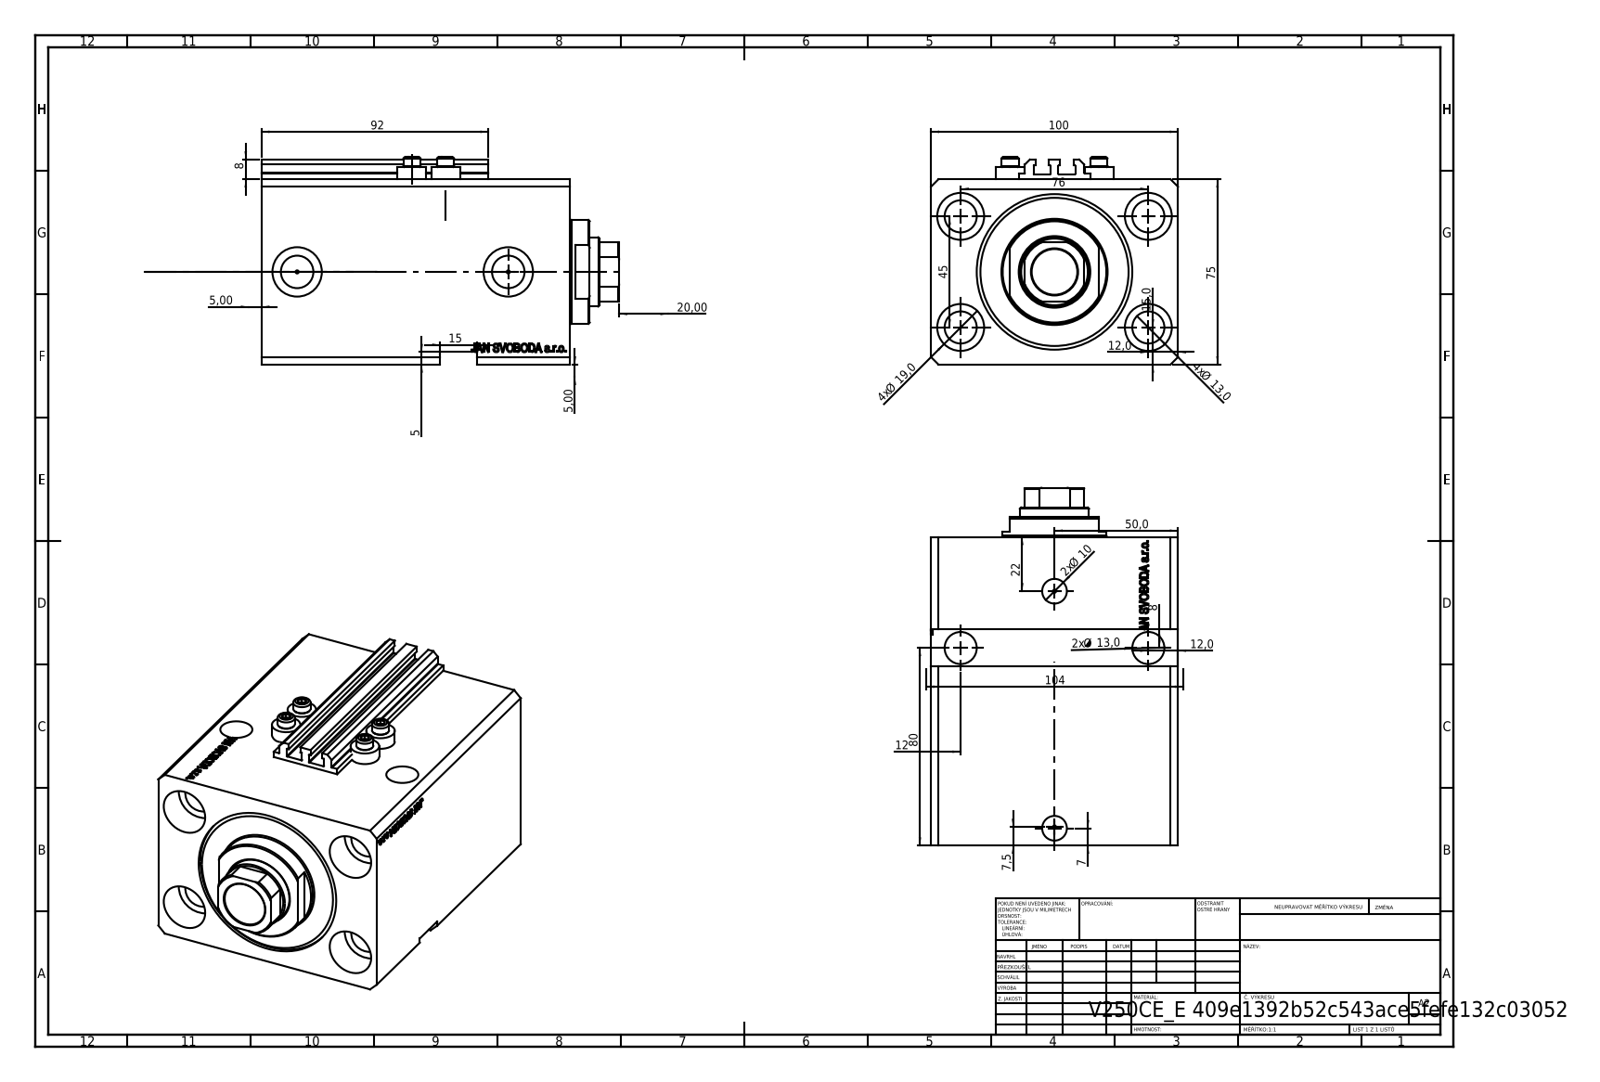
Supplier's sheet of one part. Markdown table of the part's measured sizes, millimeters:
| quantity | value |
| --- | --- |
| part name | V250CE_C_VCP; V250CE_E_Body; ALLEN BOLT V250CE; V250CE_VC_E |
| STEP written by | SolidWorks 2019 (CONFIG_CONTROL_DESIGN) |
| units | millimeters |
| bodies | 8 solids, 1088 faces (535 planar, 126 cylindrical, 427 other) |
| overall size | 144.9 × 100 × 84 |
| volume | 782 818 mm³ |
| surface area | 149 099 mm² |
| round holes (diameter × count) | 13 × 6, 1.25 × 4, 4 × 4, 19 × 4, 10 × 2, 13.16 × 2, 20 × 2, 18.5 × 1, 28 × 1, 50 × 1, 63 × 1 |
| round bosses / shafts (diameter × count) | 11.6 × 4, 7 × 4, 42 × 1 |
| partial cylindrical surfaces (radius × count) | 0.2 × 10, 13.5 × 1 |
| main face-to-face distances | 75, 100, 125, 11.9, 113.1, 98.4, 86.5, 26.6, 48.4, 5 |
| hole center spacings | 44.16, 76, 13.6, 20.72, 27.59, 33.62, 36, 38.48 |
